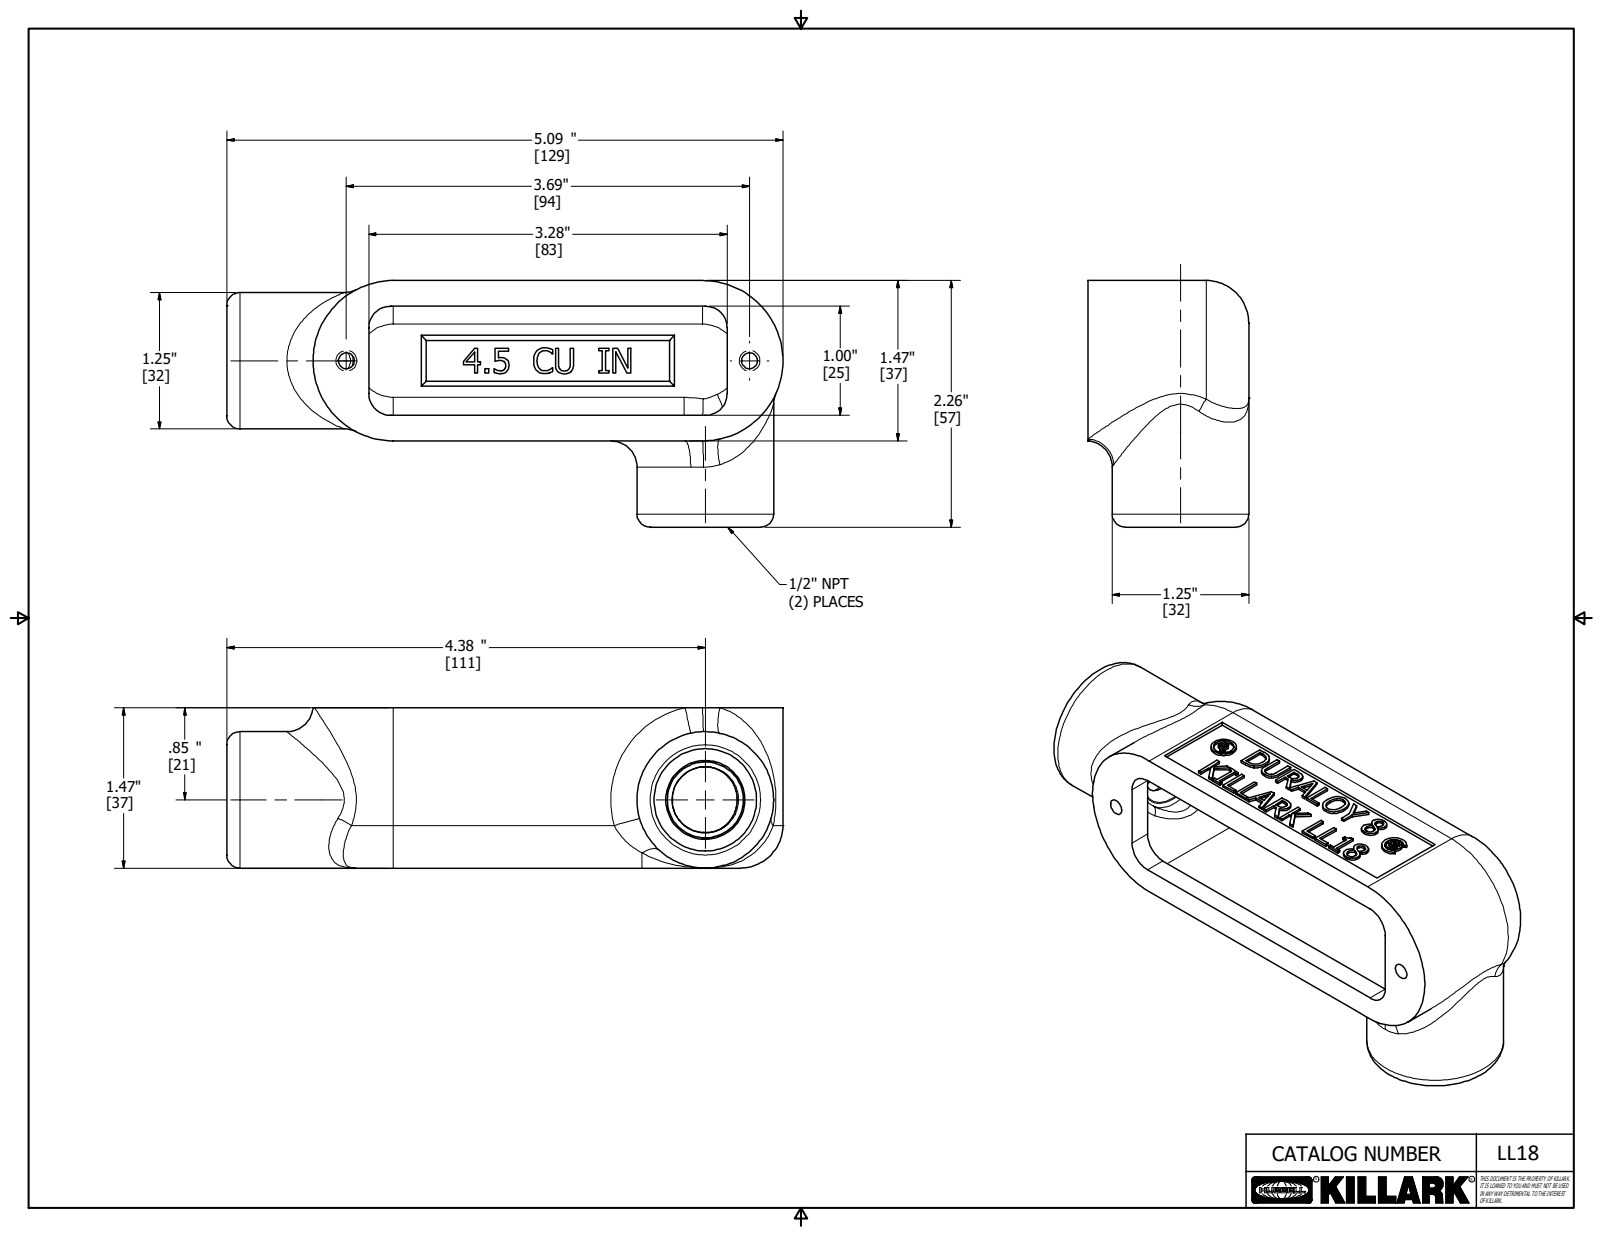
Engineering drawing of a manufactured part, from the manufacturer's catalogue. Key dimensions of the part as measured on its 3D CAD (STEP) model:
Part name (STEP PRODUCT): 21724-2
STEP written by: Autodesk Inventor 2018 (AUTOMOTIVE_DESIGN)
Units: inches
Bodies: 1 solid, 492 faces (296 planar, 35 cylindrical, 161 other)
Overall size (bounding box): 5.09 × 2.26 × 1.47
Volume: 4.729 in³ · Surface area: 47.95 in²
Round holes (diameter × count): ⌀0.145 ×2, ⌀0.844 ×2, ⌀0.187 ×1
Round bosses / shafts (diameter × count): ⌀1.25 ×2, ⌀0.23 ×1
Partial cylindrical surfaces — rounded edges, fillets, slot ends (radius × count): R0.2 ×6, R0.39 ×2, R0.535 ×2, R0.735 ×2, R0.007 ×1, R0.029 ×1, R0.052 ×1, R0.074 ×1
Main face-to-face distances: 1.27, 0.2, 1.47, 1.07, 1.44, 1.24, 0.17, 0.035, 0.235, 1.235
Hole centre spacings: 2.552, 3.69
